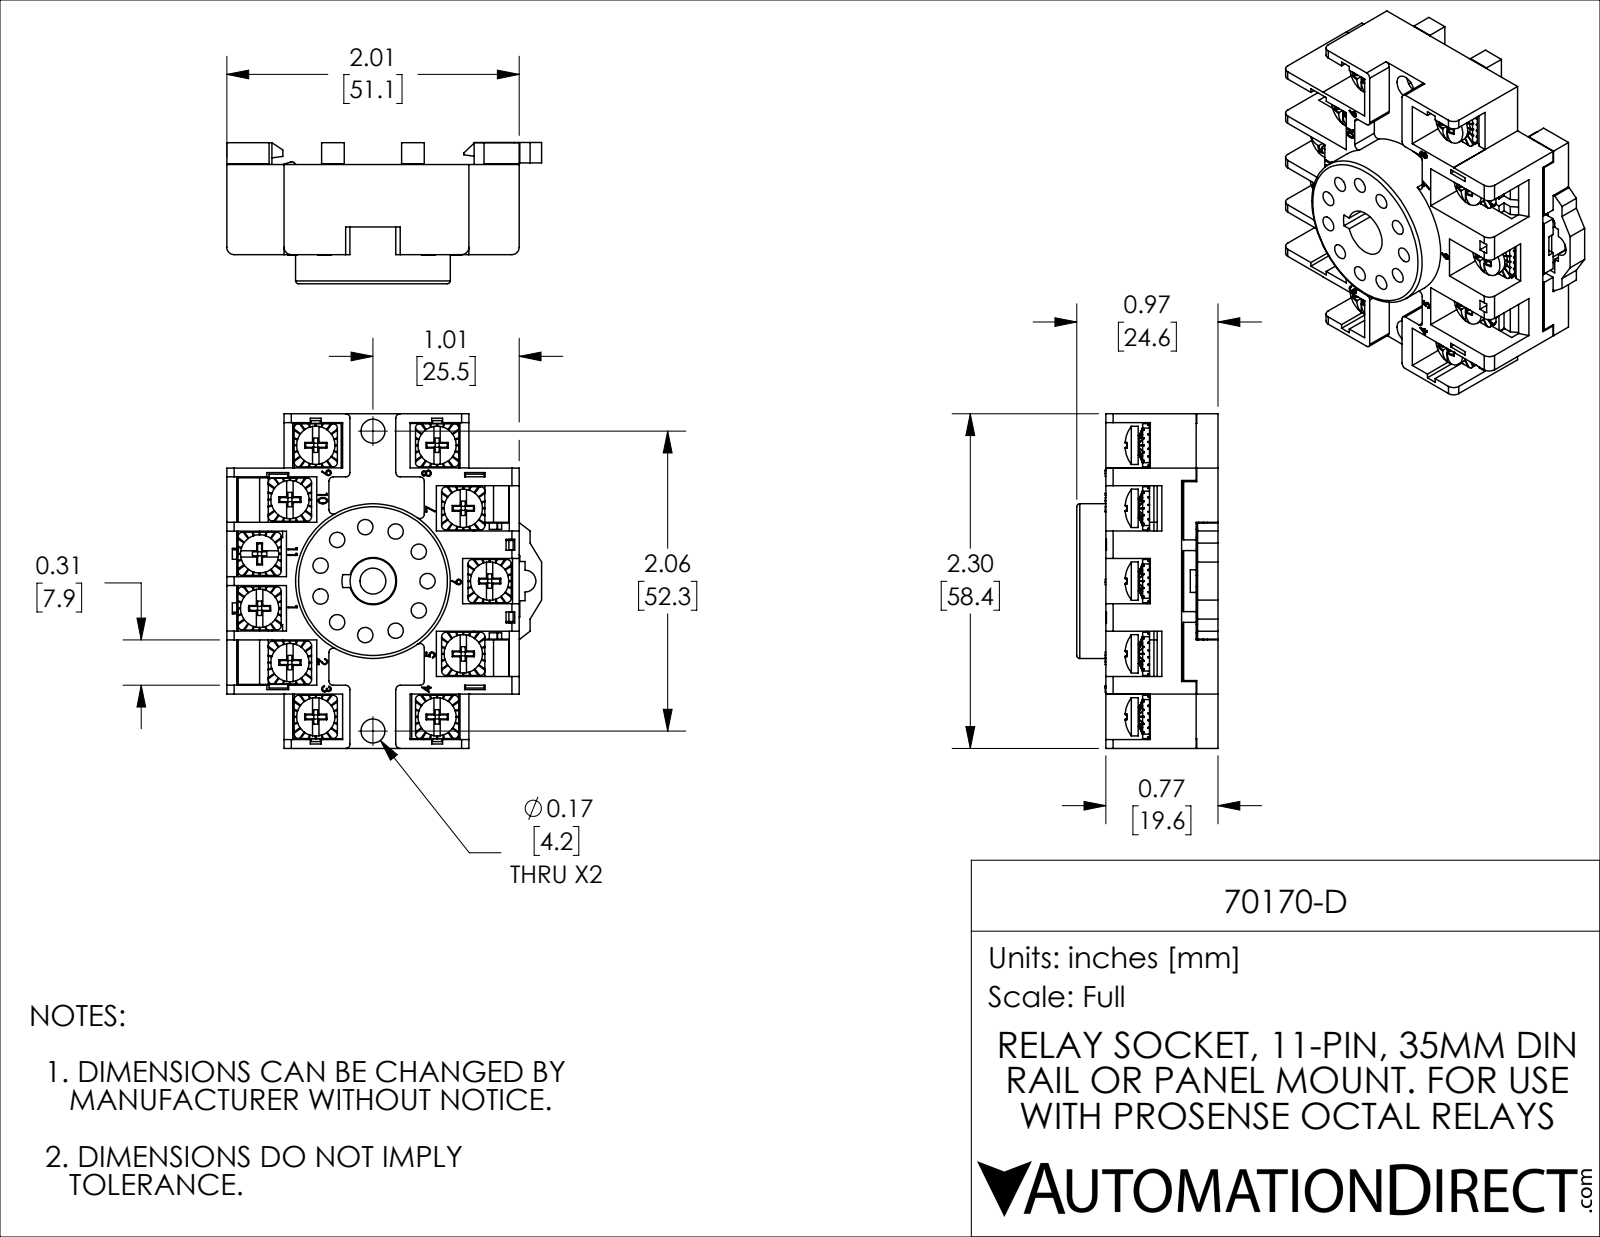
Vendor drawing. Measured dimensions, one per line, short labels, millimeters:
name: 70170-D
written by: SolidWorks 2021 (CONFIG_CONTROL_DESIGN)
unit: mm
bodies: 26 solids, 1502 faces (975 planar, 297 cylindrical, 230 other)
size: 58.42 × 54.99 × 24.66
volume: 31 829 mm³; area: 28 076 mm²
holes: 12× ⌀3.51, 11× ⌀4.57, 6× ⌀2.67, 5× ⌀2.67, 2× ⌀4.19, 1× ⌀4.52, 1× ⌀7.98, 1× ⌀8.26, 1× ⌀10.79
bosses: 11× ⌀6.68, 11× ⌀3.53, 11× ⌀3.41, 1× ⌀27
rounds: 65× R0.76, 24× R0.13, 4× R1.27, 3× R0.82, 2× R0.25, 2× R0.51, 2× R2.22, 1× R0.38
face distances: 7.36, 1.15, 8.51, 1.55, 1.53, 47.4, 9.47, 7.77, 8.38, 9.49
hole spacings: 18.84, 10.85, 10.29, 14.4, 9.53, 5.35, 5.36, 9.5
